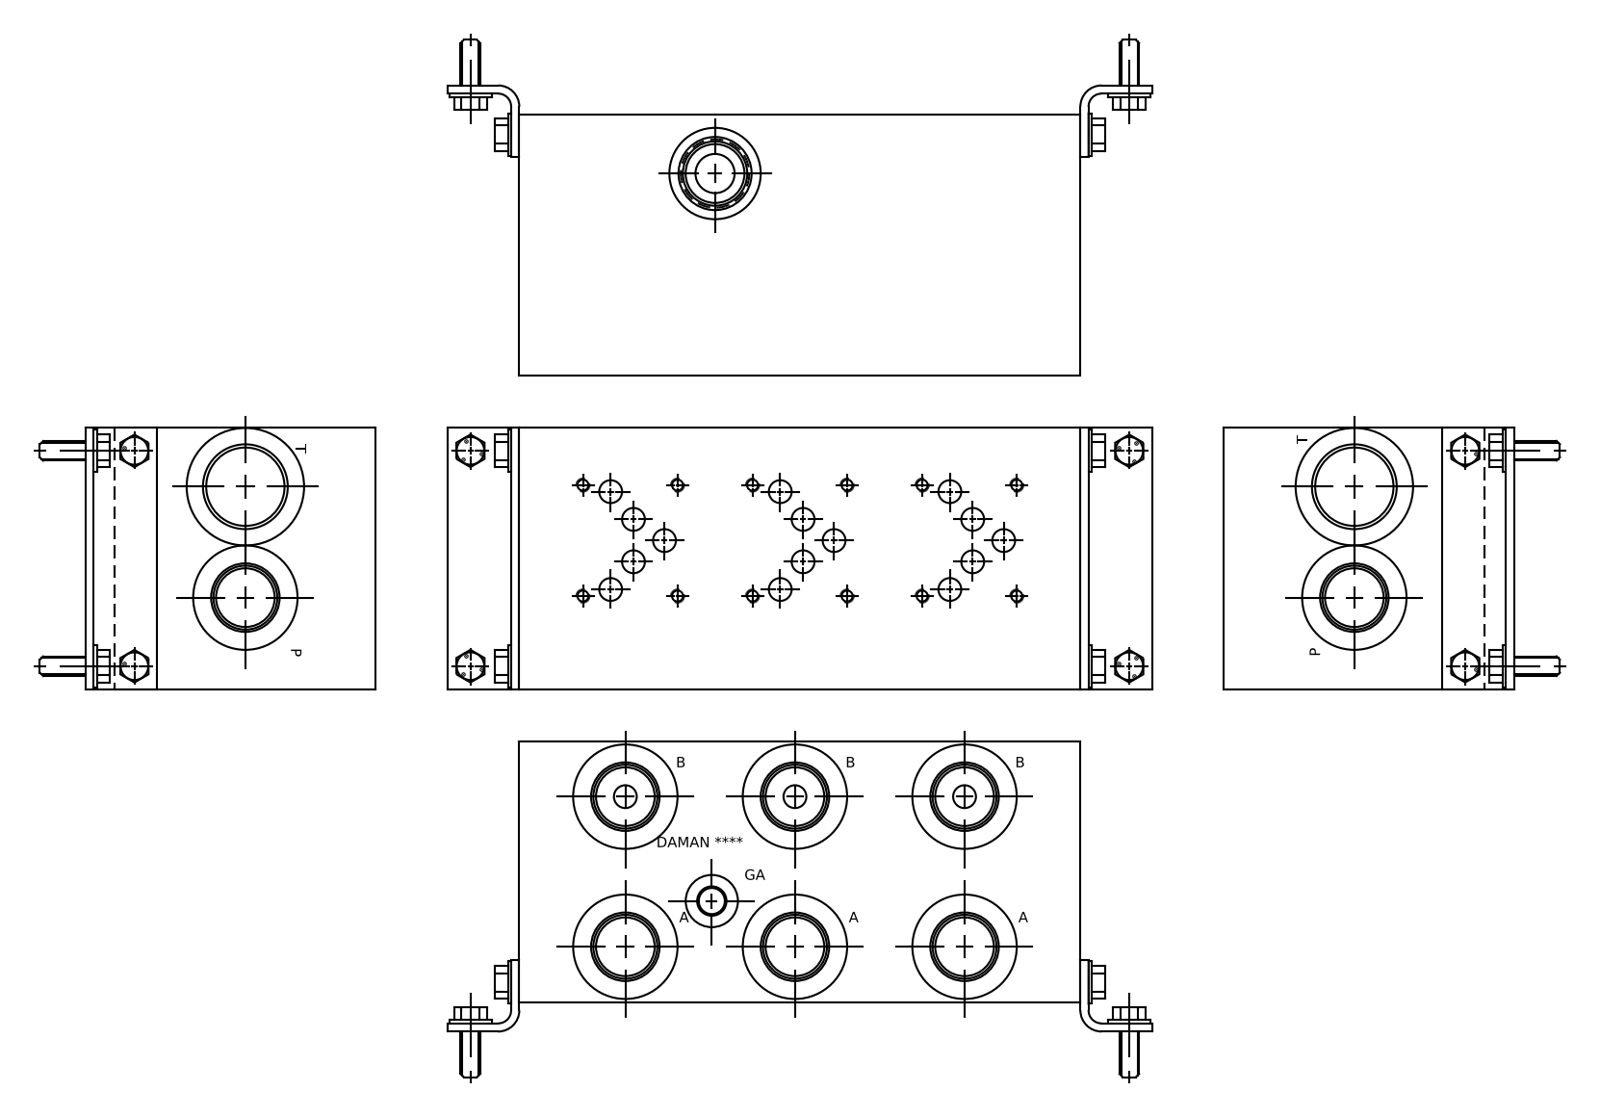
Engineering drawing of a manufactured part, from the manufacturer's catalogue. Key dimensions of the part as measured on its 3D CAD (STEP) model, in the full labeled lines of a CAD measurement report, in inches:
Part name (STEP PRODUCT): Part_AD05JP033S~C_3D
STEP written by: Autodesk Inventor 2021 (AUTOMOTIVE_DESIGN)
Units: inches
Bodies: 1 solid, 784 faces (387 planar, 113 cylindrical, 284 other)
Overall size (bounding box): 10.75 × 5 × 5
Volume: 244 in³ · Surface area: 349.8 in²
Round holes (diameter × count): ⌀0.201 ×12, ⌀0.25 ×12, ⌀1.313 ×8, ⌀1.231 ×7, ⌀1.329 ×7, ⌀1.928 ×7, ⌀0.406 ×6, ⌀0.438 ×6, ⌀1.125 ×6, ⌀0.375 ×5, ⌀1.398 ×5, ⌀0.312 ×2
Main face-to-face distances: 5, 10.75, 0.031, 4.969, 10.719, 10.688, 0.75, 0.781, 4.219, 9.969
Hole centre spacings: 3.25, 6.5, 2.374, 2.125, 0.72, 1.394, 1.413, 1.973
